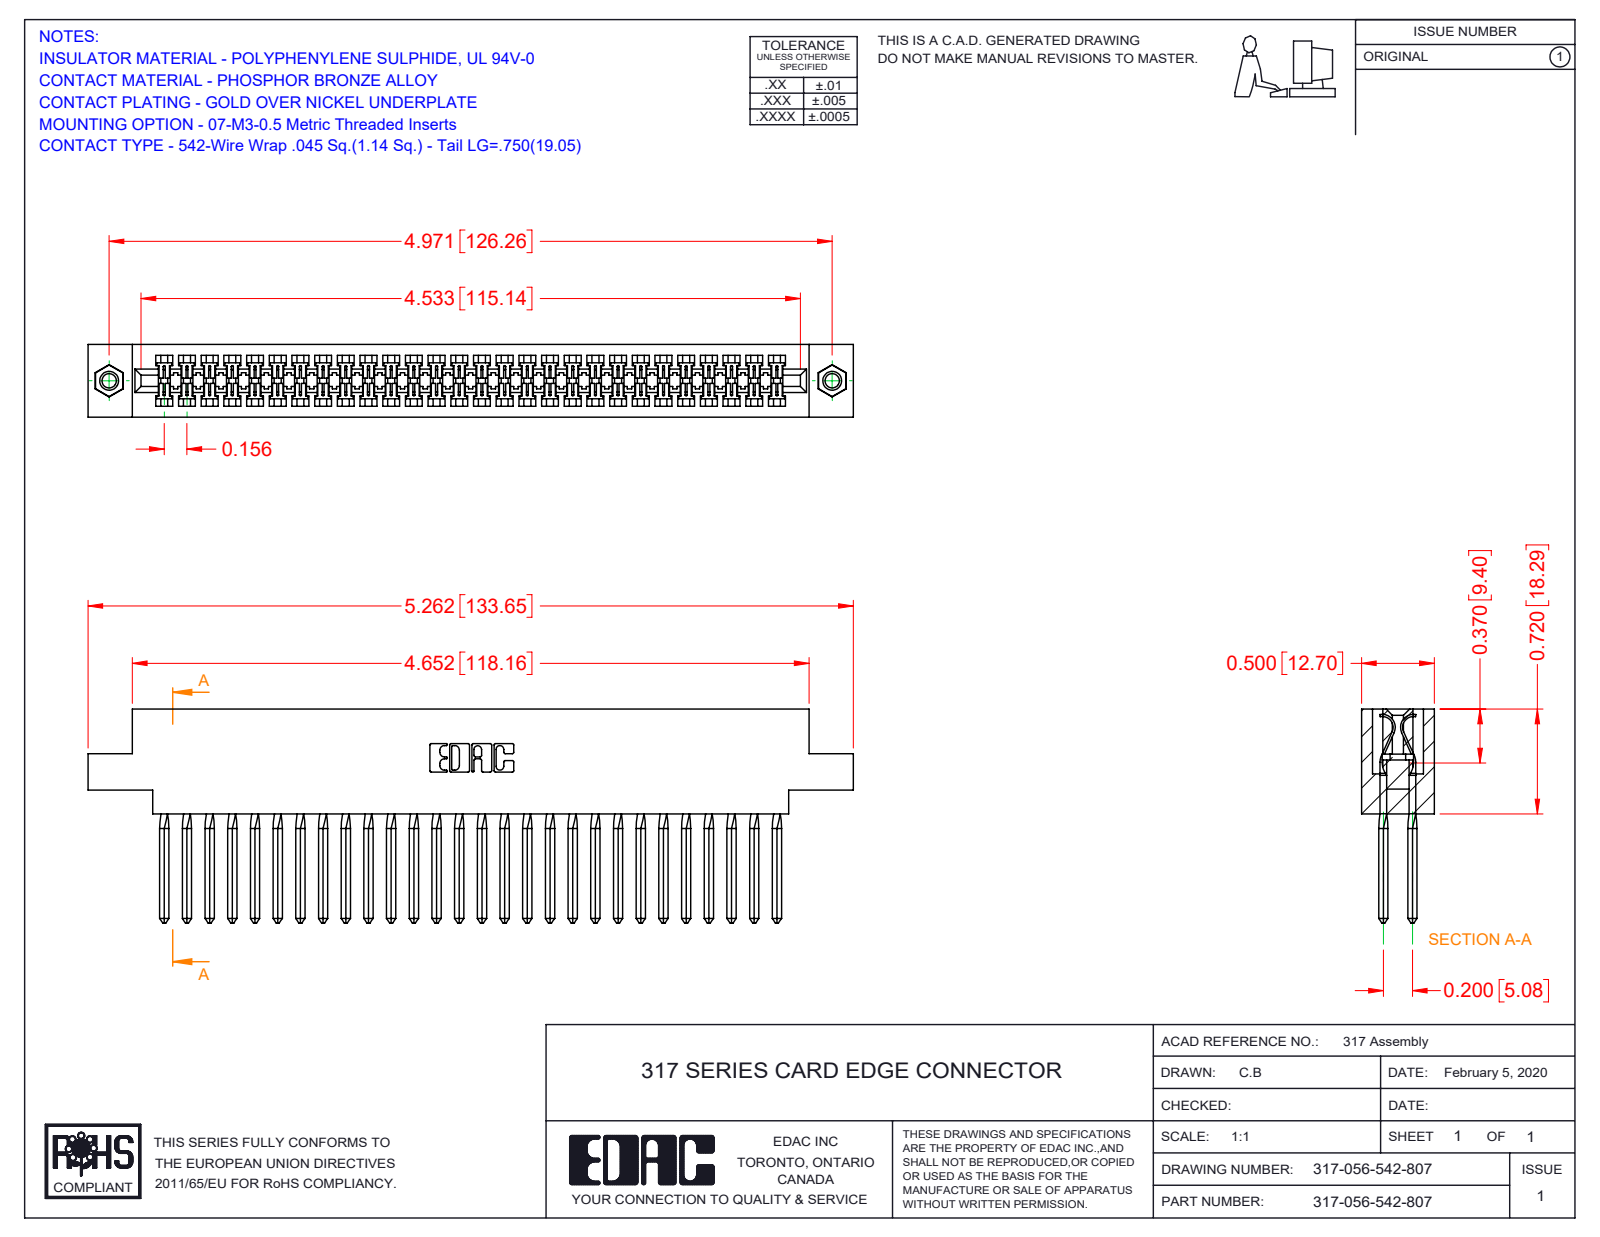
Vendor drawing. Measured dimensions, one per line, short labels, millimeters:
name: 317-290-003_542; 317 Part_.156 Dia - TI; 317-056-542-807; 345-250-001_345-250-005-103
written by: SolidWorks 2016 (CONFIG_CONTROL_DESIGN)
unit: mm
bodies: 59 solids, 3354 faces (2666 planar, 448 cylindrical, 240 other)
size: 133.7 × 37.3 × 12.7
volume: 21 430 mm³; area: 29 390 mm²
holes: 2× ⌀2.5, 2× ⌀3.2, 2× ⌀4
bosses: 2× ⌀3.9
rounds: 112× R0.2, 22× R0.3, 6× R0.2, 6× R0.8, 3× R0.7, 2× R1.9, 2× R2.3, 2× R2.5
face distances: 12.7, 1.9, 10.8, 8.9, 5.1, 2.8, 2.9, 1.2, 3.5, 3.3
hole spacings: 126.3
